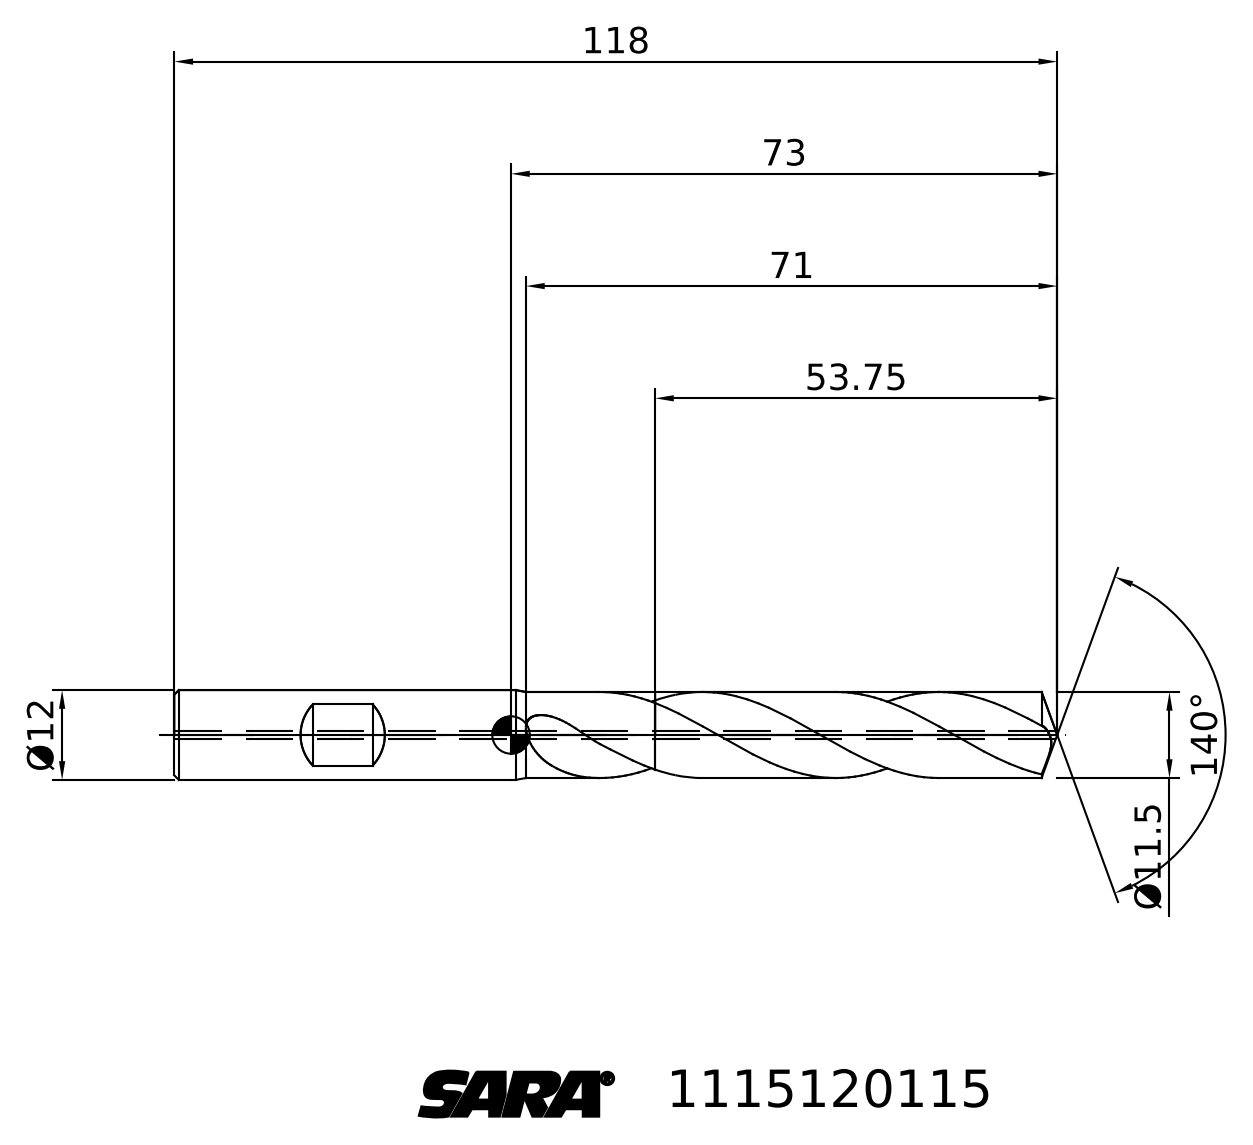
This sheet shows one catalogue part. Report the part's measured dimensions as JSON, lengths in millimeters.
{"step_written_by": "TDM (AUTOMOTIVE_DESIGN)", "units": "millimeters", "bodies": {"solids": 2, "faces": 29, "planar": 6, "cylindrical": 0, "other": 23}, "overall_size": [118, 21.45, 12], "volume_mm3": 10093, "surface_area_mm2": 4808, "face_to_face_distances": [64.25]}
